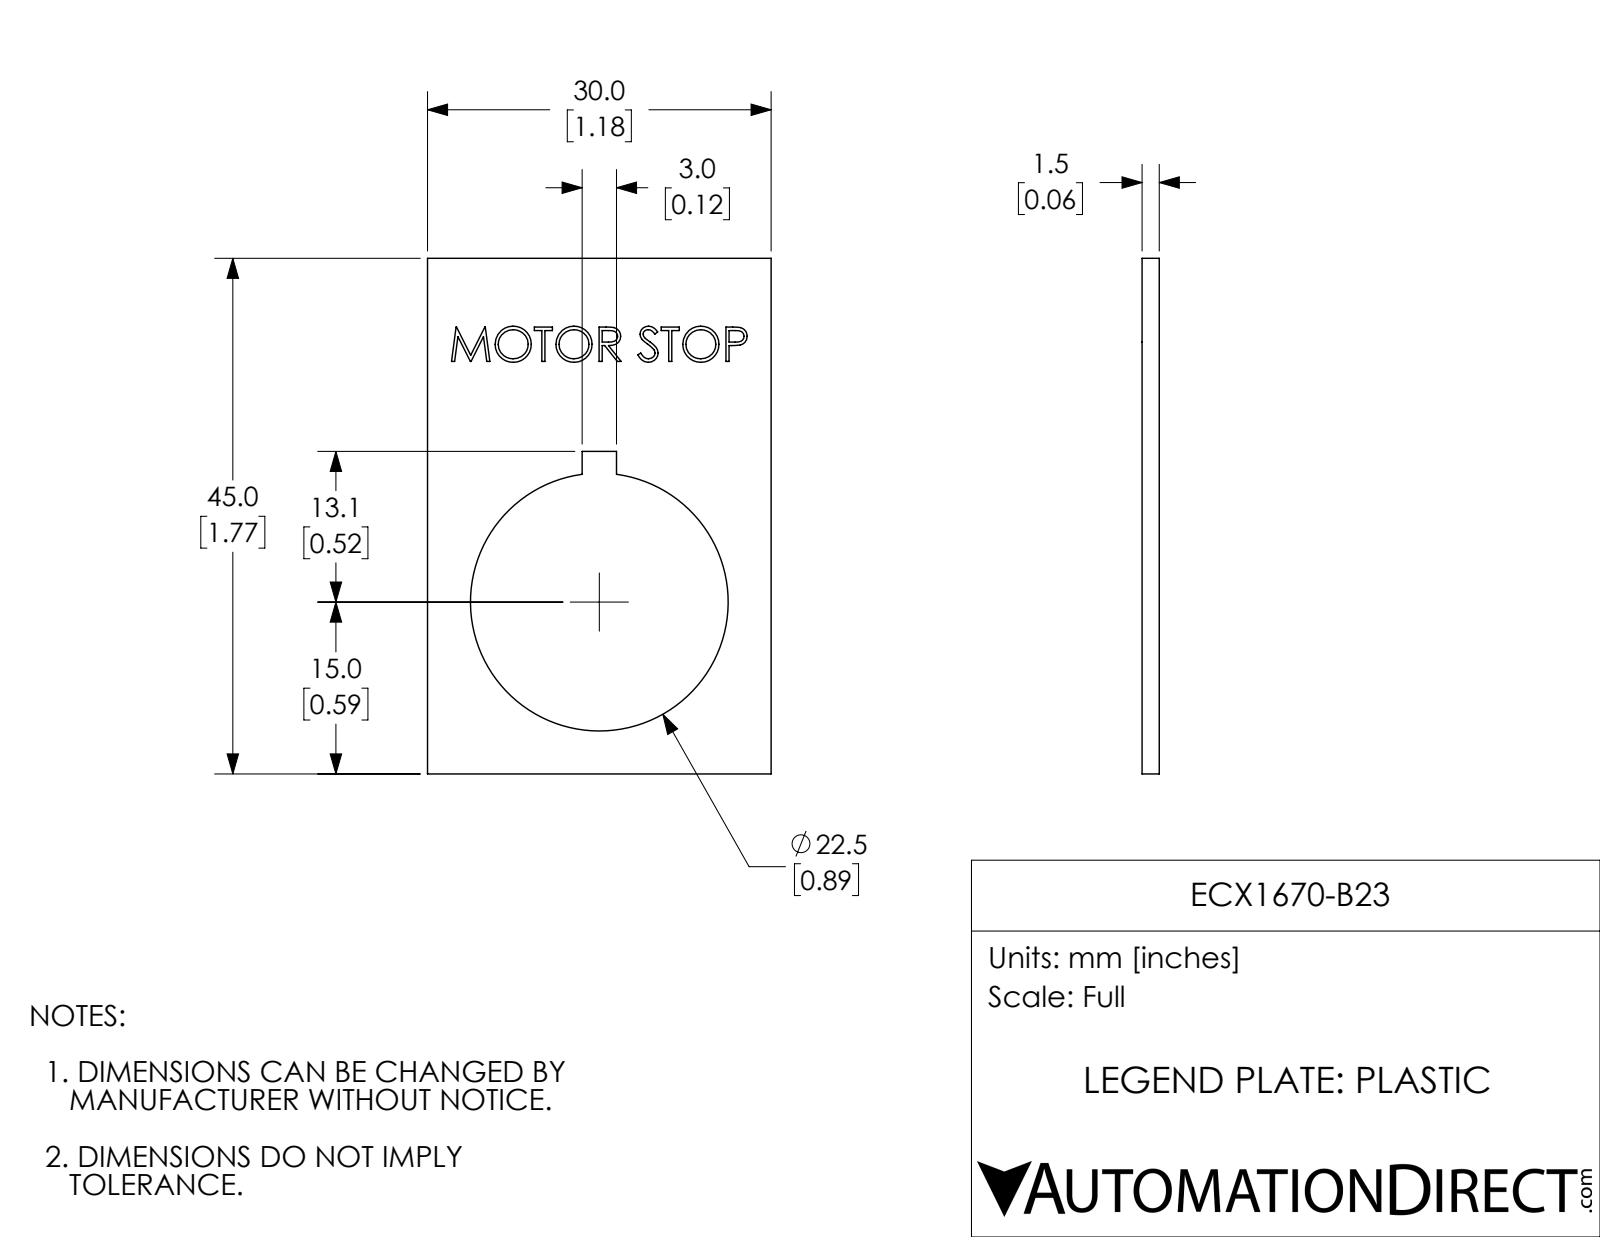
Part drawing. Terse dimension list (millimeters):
name: ECX1670-B23
written by: SolidWorks 2017 (AUTOMOTIVE_DESIGN)
unit: mm
bodies: 1 solid, 126 faces (73 planar, 3 cylindrical, 50 other)
size: 45 × 30 × 1.5
volume: 1 400 mm³; area: 2 234 mm²
holes: 1× ⌀22.5
face distances: 1.5, 30, 45, 1.5, 13.5, 16.5, 28.1, 16.8, 3, 11.1
